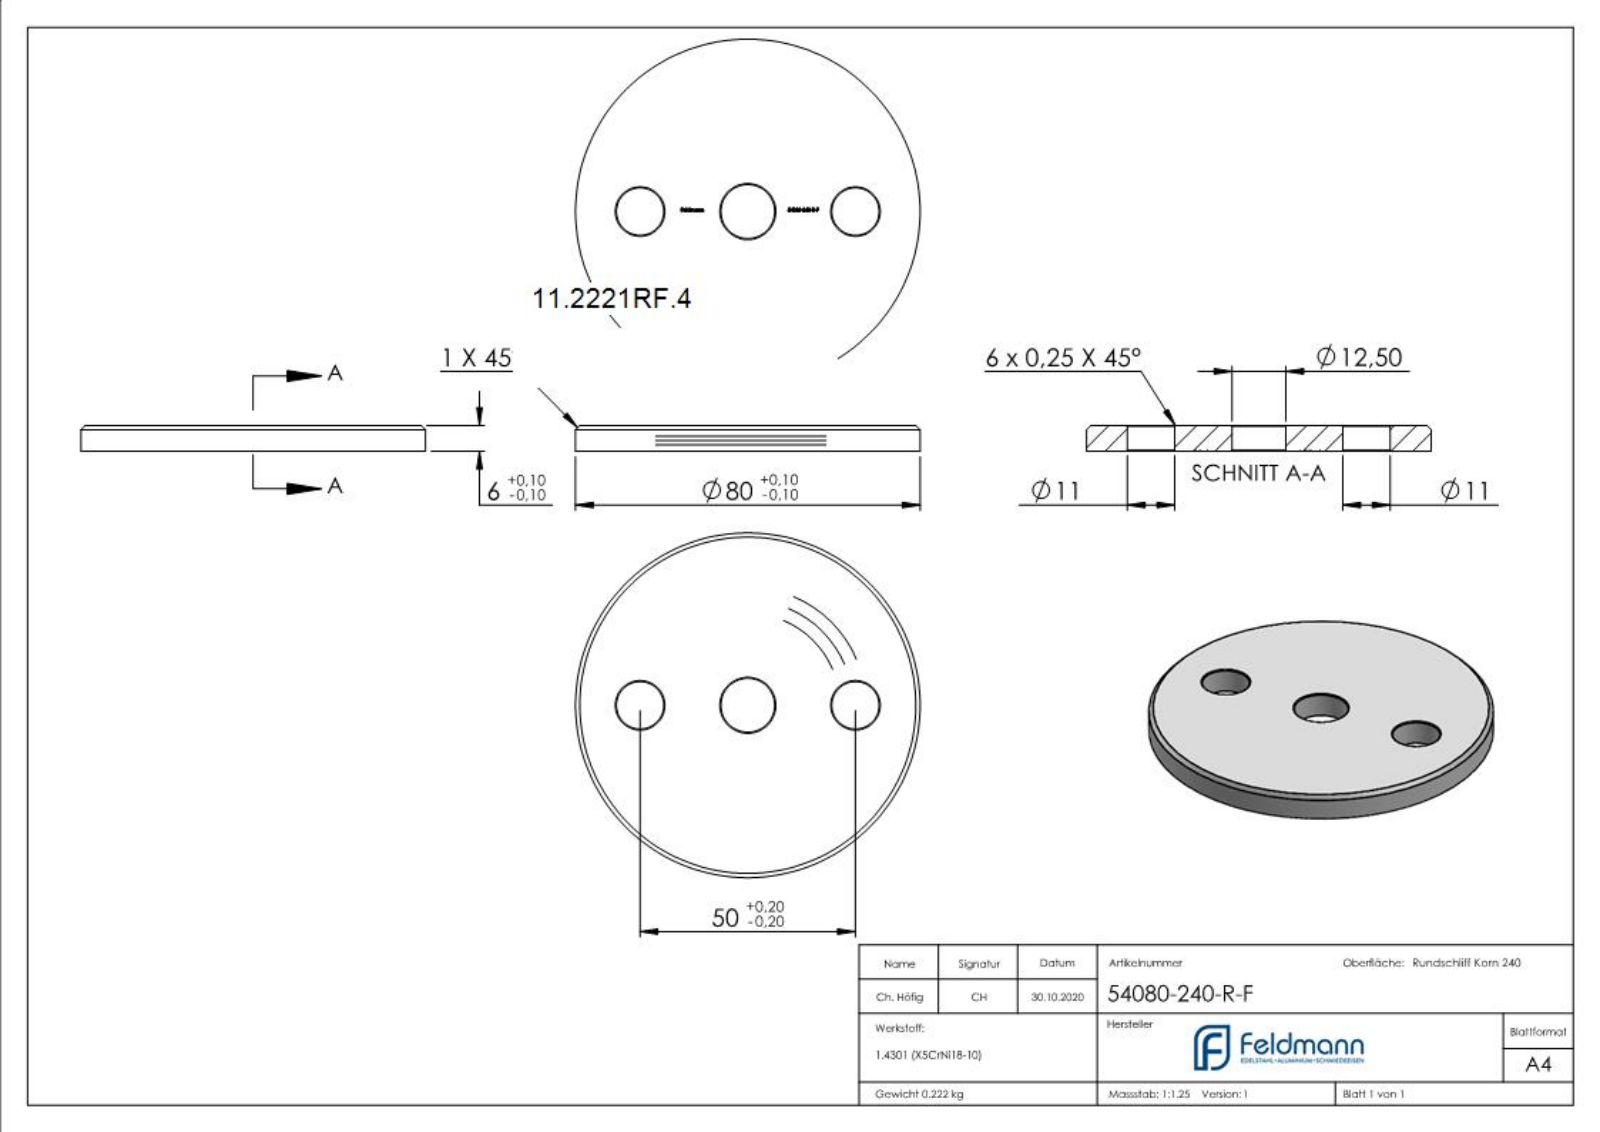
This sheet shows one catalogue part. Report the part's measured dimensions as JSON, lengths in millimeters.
{"part_name": "54080-240-R-F", "step_written_by": "SolidWorks 2018 (CONFIG_CONTROL_DESIGN)", "units": "millimeters", "bodies": {"solids": 1, "faces": 292, "planar": 159, "cylindrical": 8, "other": 125}, "overall_size": [80, 80, 6], "volume_mm3": 28151, "surface_area_mm2": 11413, "round_holes": [[11, 2], [12.5, 1]], "round_bosses_or_shafts": [[80, 1]], "face_to_face_distances": [6, 5.9, 0.53, 1.21, 29.23, 1.28, 29.16, 0.44, 0.32, 1.78], "hole_center_spacings": [25, 50]}
